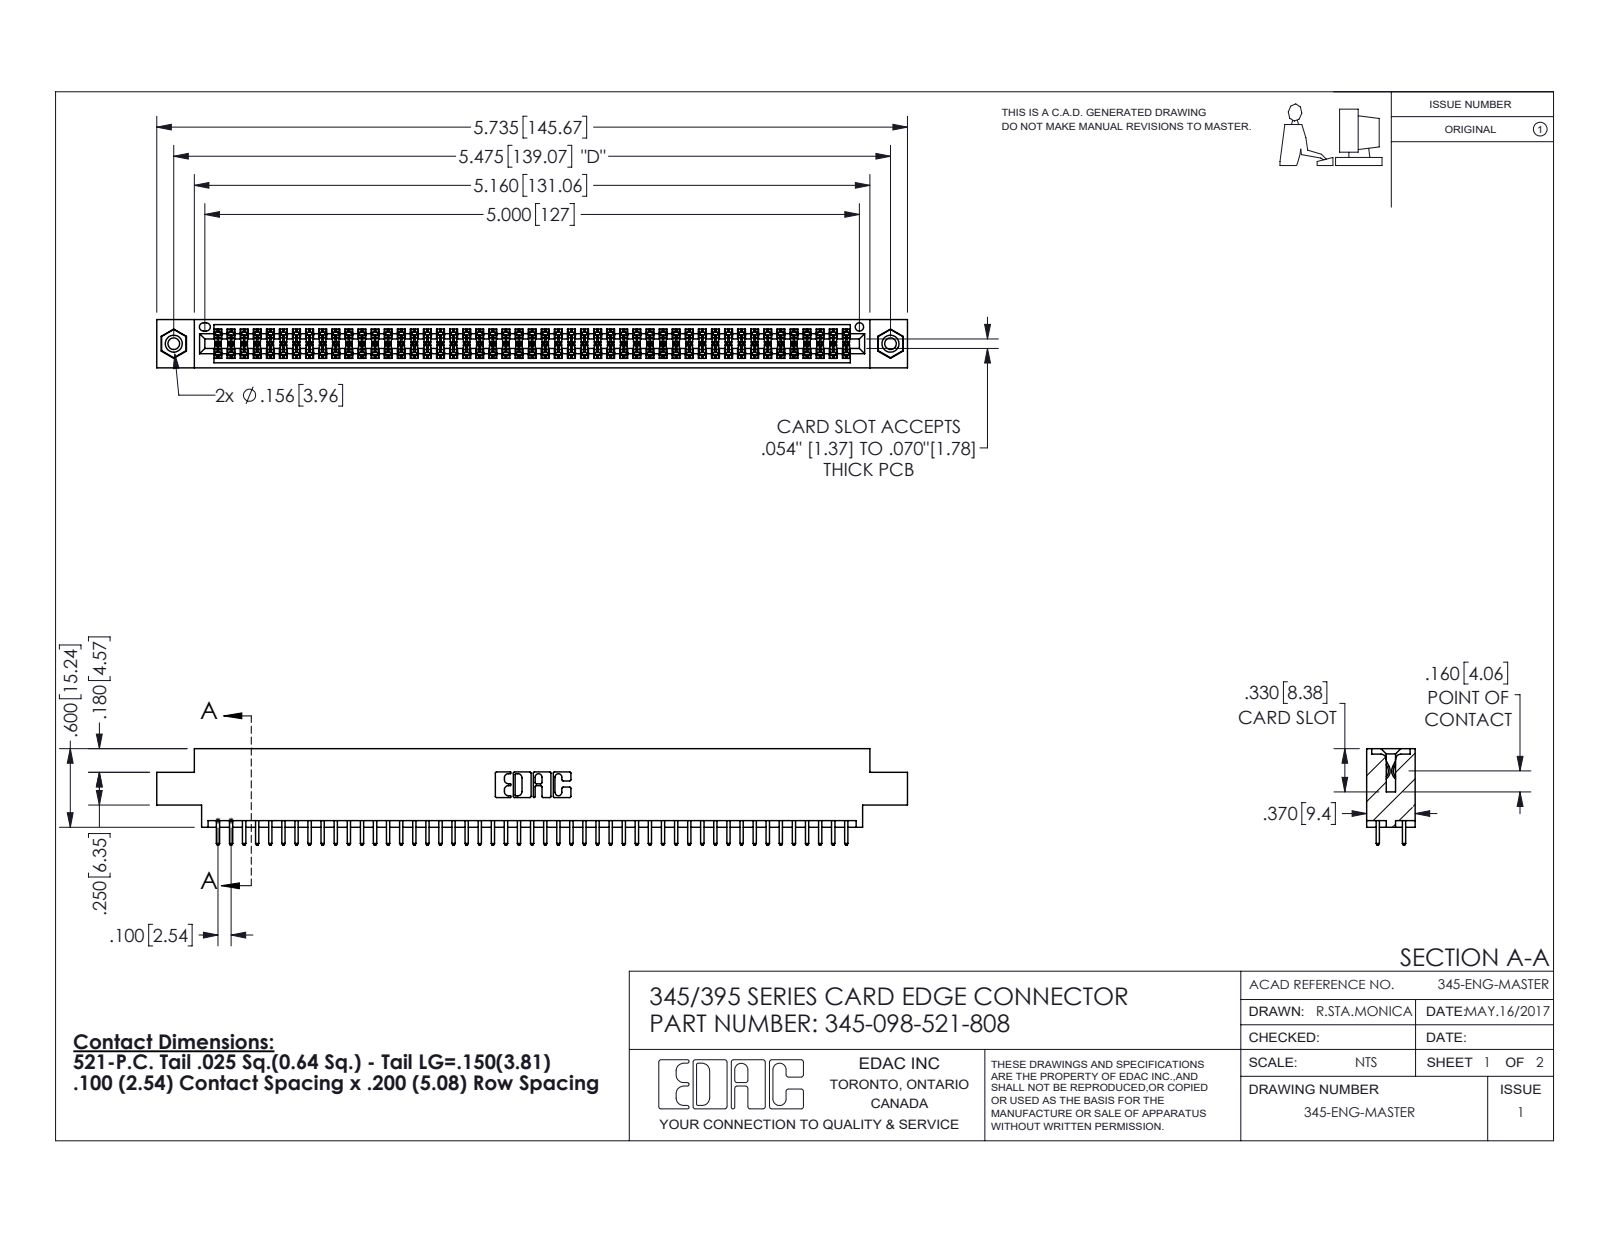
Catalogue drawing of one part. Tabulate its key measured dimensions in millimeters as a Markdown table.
| quantity | value |
| --- | --- |
| part name | 345-250-001_345-250-003-102; 345 Part_0.170 Offset - 0.156 Dia-TI; 345-292-001_345-293-121; 345-098-521-808 |
| STEP written by | SolidWorks 2016 (CONFIG_CONTROL_DESIGN) |
| units | millimeters |
| bodies | 101 solids, 5090 faces (3350 planar, 1724 cylindrical, 16 other) |
| overall size | 145.7 × 18.7 × 9.4 |
| volume | 14 100 mm³ |
| surface area | 20 810 mm² |
| round holes (diameter × count) | 2.3 × 2, 3.2 × 2, 4 × 2, 1.6 × 1 |
| round bosses / shafts (diameter × count) | 3.9 × 2 |
| partial cylindrical surfaces (radius × count) | 0.2 × 147, 0.3 × 98, 0.3 × 22, 0.2 × 6, 0.8 × 6, 0.7 × 3, 0.4 × 2, 0.5 × 2 |
| main face-to-face distances | 1.8, 7.6, 5.1, 9.4, 2.5, 6.9, 0.6, 5.7, 4.4, 3.8 |
| hole center spacings | 6.9, 133.1, 139.1 |
